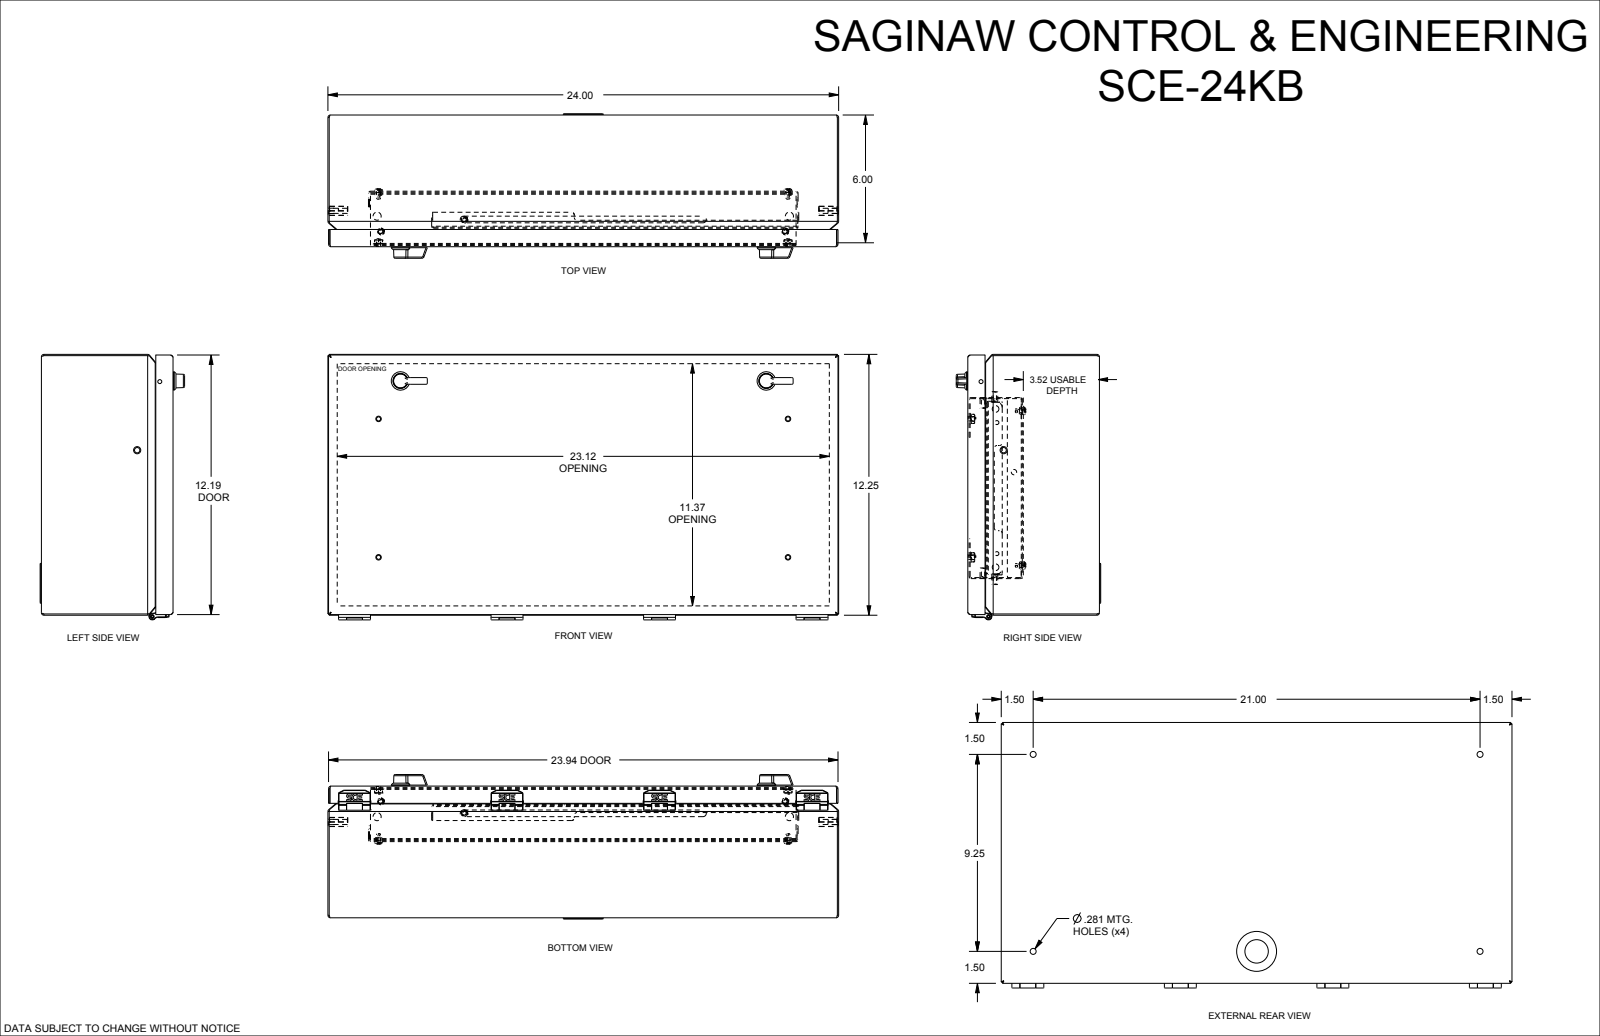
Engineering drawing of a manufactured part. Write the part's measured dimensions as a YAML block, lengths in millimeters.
part_name: "SCE-24KB-REV-1"
step_written_by: "SolidWorks 2022 (AUTOMOTIVE_DESIGN)"
units: millimeters
bodies: {solids: 77, faces: 3801, planar: 1701, cylindrical: 1316, other: 784}
overall_size: [609.8, 316.7, 172.4]
volume: 1614000
surface_area: 2206000
round_holes:
  - {diameter: 4.3, count: 8}
  - {diameter: 4, count: 5}
  - {diameter: 4.8, count: 5}
  - {diameter: 6.4, count: 5}
  - {diameter: 0.5, count: 4}
  - {diameter: 2.5, count: 4}
  - {diameter: 5.5, count: 4}
  - {diameter: 7.2, count: 4}
  - {diameter: 4, count: 3}
  - {diameter: 6.8, count: 3}
  - {diameter: 3.7, count: 2}
  - {diameter: 4, count: 2}
round_bosses_or_shafts:
  - {diameter: 12.2, count: 8}
  - {diameter: 4.1, count: 8}
  - {diameter: 8.6, count: 5}
  - {diameter: 6.3, count: 5}
  - {diameter: 4.8, count: 5}
  - {diameter: 6.6, count: 4}
  - {diameter: 6.5, count: 4}
  - {diameter: 6, count: 4}
partial_cylinders:
  - {radius: 0.2, count: 64}
  - {radius: 0.3, count: 54}
  - {radius: 0.8, count: 52}
  - {radius: 0.5, count: 48}
  - {radius: 0.6, count: 48}
  - {radius: 0.3, count: 42}
  - {radius: 0.4, count: 38}
  - {radius: 0.5, count: 20}
face_to_face_distances: [1.5, 1.5, 1.2, 155.6, 157.1, 154.1, 155.6, 63.5, 309.7, 92.1]
hole_center_spacings: [182, 364.1, 546.1, 436.6, 488.7, 488.8, 9.7, 9.7]
